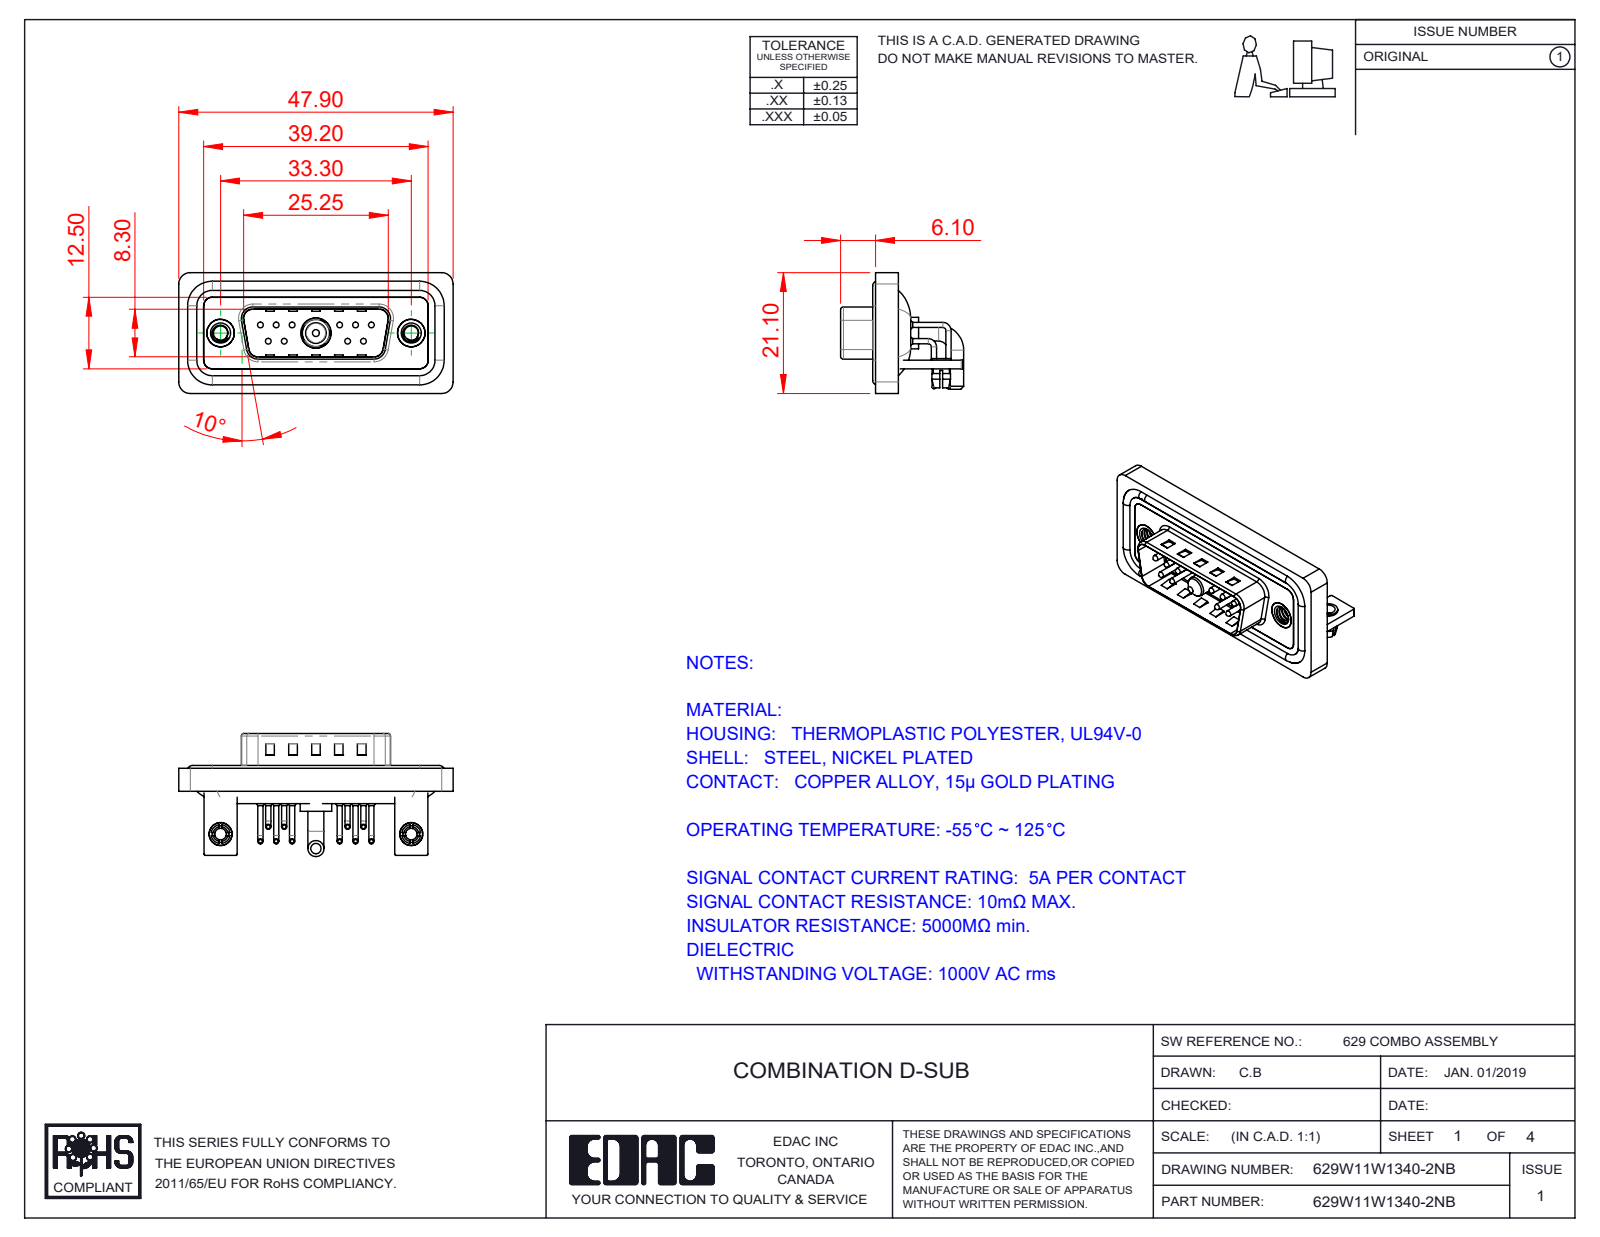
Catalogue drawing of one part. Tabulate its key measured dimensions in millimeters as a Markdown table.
| quantity | value |
| --- | --- |
| part name | 629Combo Housing_11W1; 629W11W1340-2NB; 629Combo Board Lock; 629Combo Contact Row 1 (+7 more) |
| STEP written by | SolidWorks 2023 (CONFIG_CONTROL_DESIGN) |
| units | millimeters |
| bodies | 23 solids, 1733 faces (904 planar, 619 cylindrical, 210 other) |
| overall size | 47.9 × 21.5 × 21.1 |
| volume | 5 898 mm³ |
| surface area | 10 079 mm² |
| round holes (diameter × count) | 2 × 12, 0.75 × 10, 1.6 × 10, 2.5 × 4, 3.2 × 2, 4 × 2, 4.8 × 2, 5 × 2, 4.85 × 1, 5.3 × 1 |
| round bosses / shafts (diameter × count) | 0.9 × 20, 1.5 × 10, 1 × 10, 0.65 × 10, 1.6 × 4, 4.9 × 2, 4 × 2, 3.4 × 2 |
| partial cylindrical surfaces (radius × count) | 2 × 21, 1.5 × 18, 0.25 × 16, 1.01 × 10, 0.5 × 9, 1.6 × 8, 1 × 7, 0.6 × 4 |
| main face-to-face distances | 0.4, 0.8, 1.5, 2.9, 2.1, 1.1, 1.6, 1.2, 3.7, 4.1 |
| hole center spacings | 3.16, 2.77, 13.85, 11.08, 16.62, 5.03, 5.04, 5.54 |
